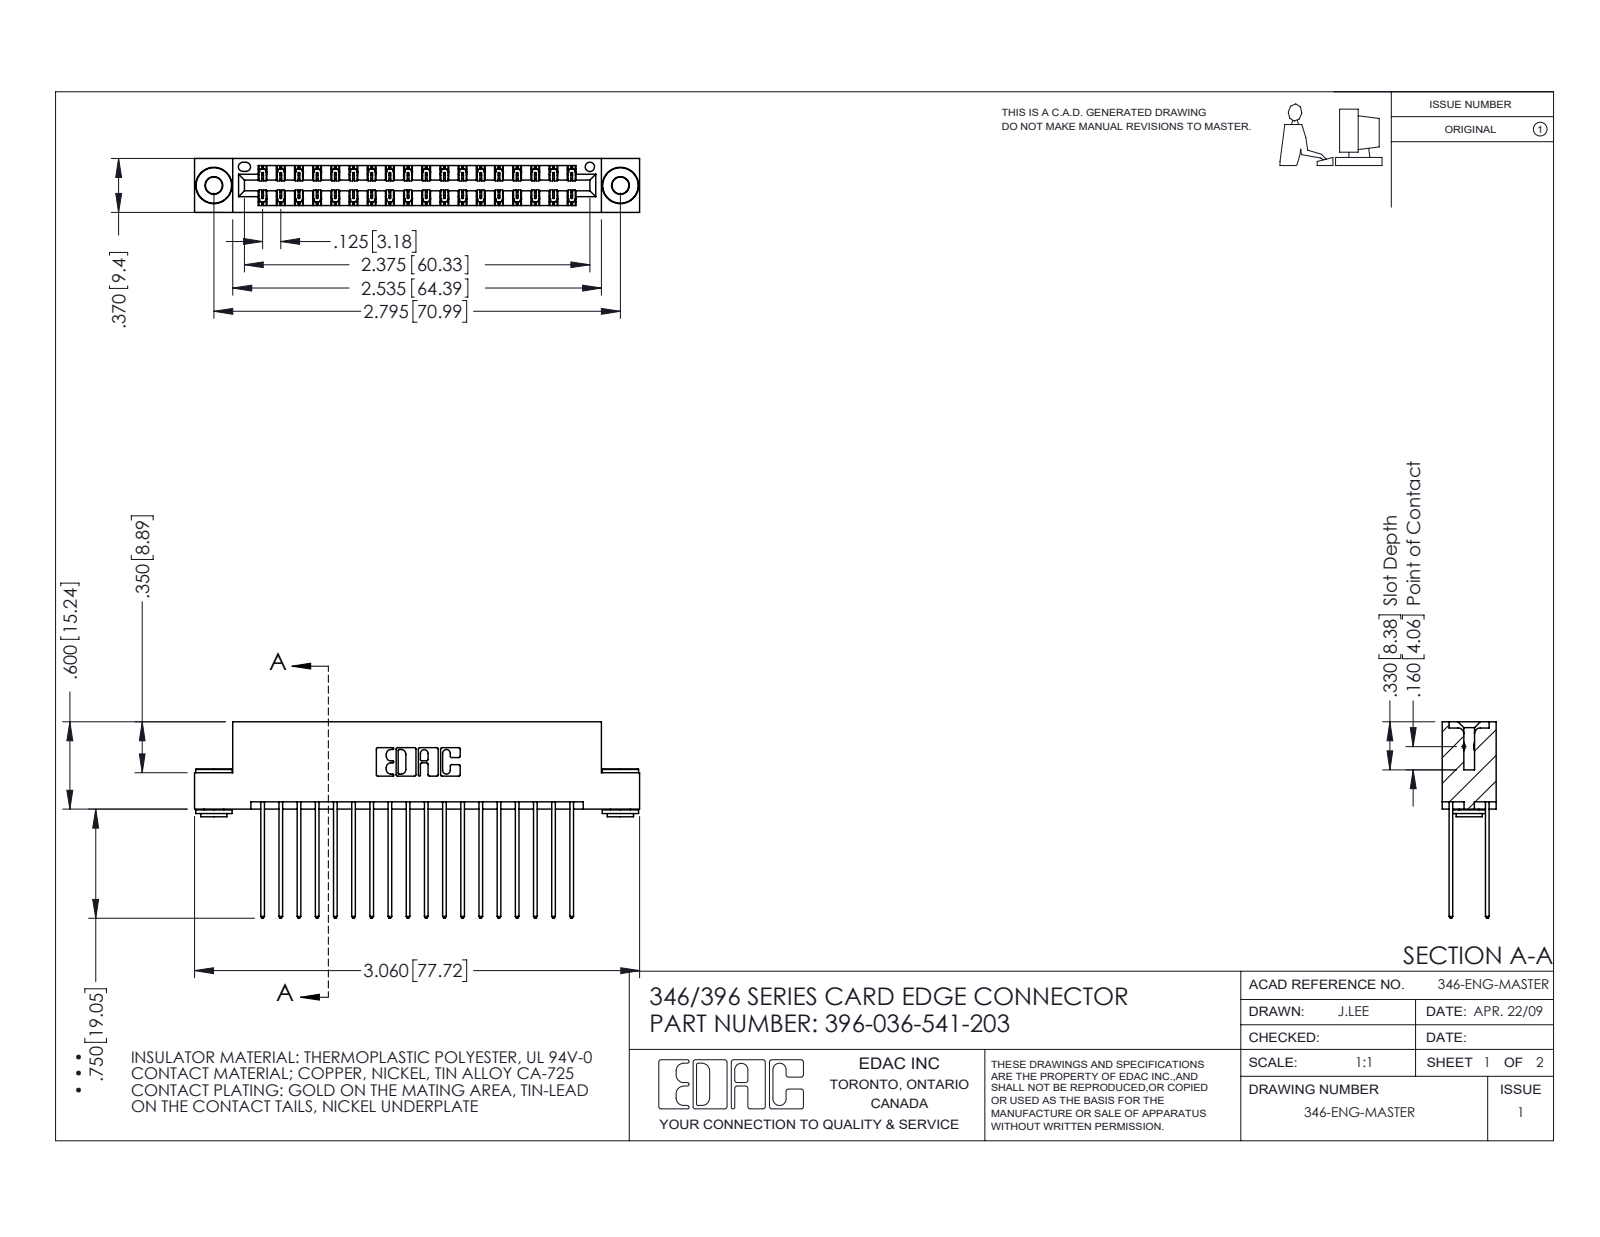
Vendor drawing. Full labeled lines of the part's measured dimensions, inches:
Part name (STEP PRODUCT): 346 Part_Flush Mounting Lugs - 0.156 Dia-TH; 345-292-001_345-293-141; 345-250-002_345-250-002-102; 396-036-541-203
STEP written by: SolidWorks 2016 (CONFIG_CONTROL_DESIGN)
Units: inches
Bodies: 39 solids, 2032 faces (1346 planar, 678 cylindrical, 8 other)
Overall size (bounding box): 3.06 × 1.35 × 0.37
Volume: 0.465 in³ · Surface area: 17.51 in²
Round holes (diameter × count): ⌀0.116 ×2, ⌀0.156 ×2, ⌀0.064 ×1
Round bosses / shafts (diameter × count): ⌀0.25 ×2, ⌀0.18 ×2, ⌀0.136 ×2
Partial cylindrical surfaces — rounded edges, fillets, slot ends (radius × count): R0.006 ×54, R0.01 ×36, R0.01 ×22, R0.007 ×6, R0.031 ×6, R0.026 ×3, R0.014 ×2, R0.022 ×2
Main face-to-face distances: 0.048, 0.322, 0.25, 0.025, 0.072, 0.298, 0.37, 0.275, 0.225, 0.148
Hole centre spacings: 0.246, 2.588, 2.795
